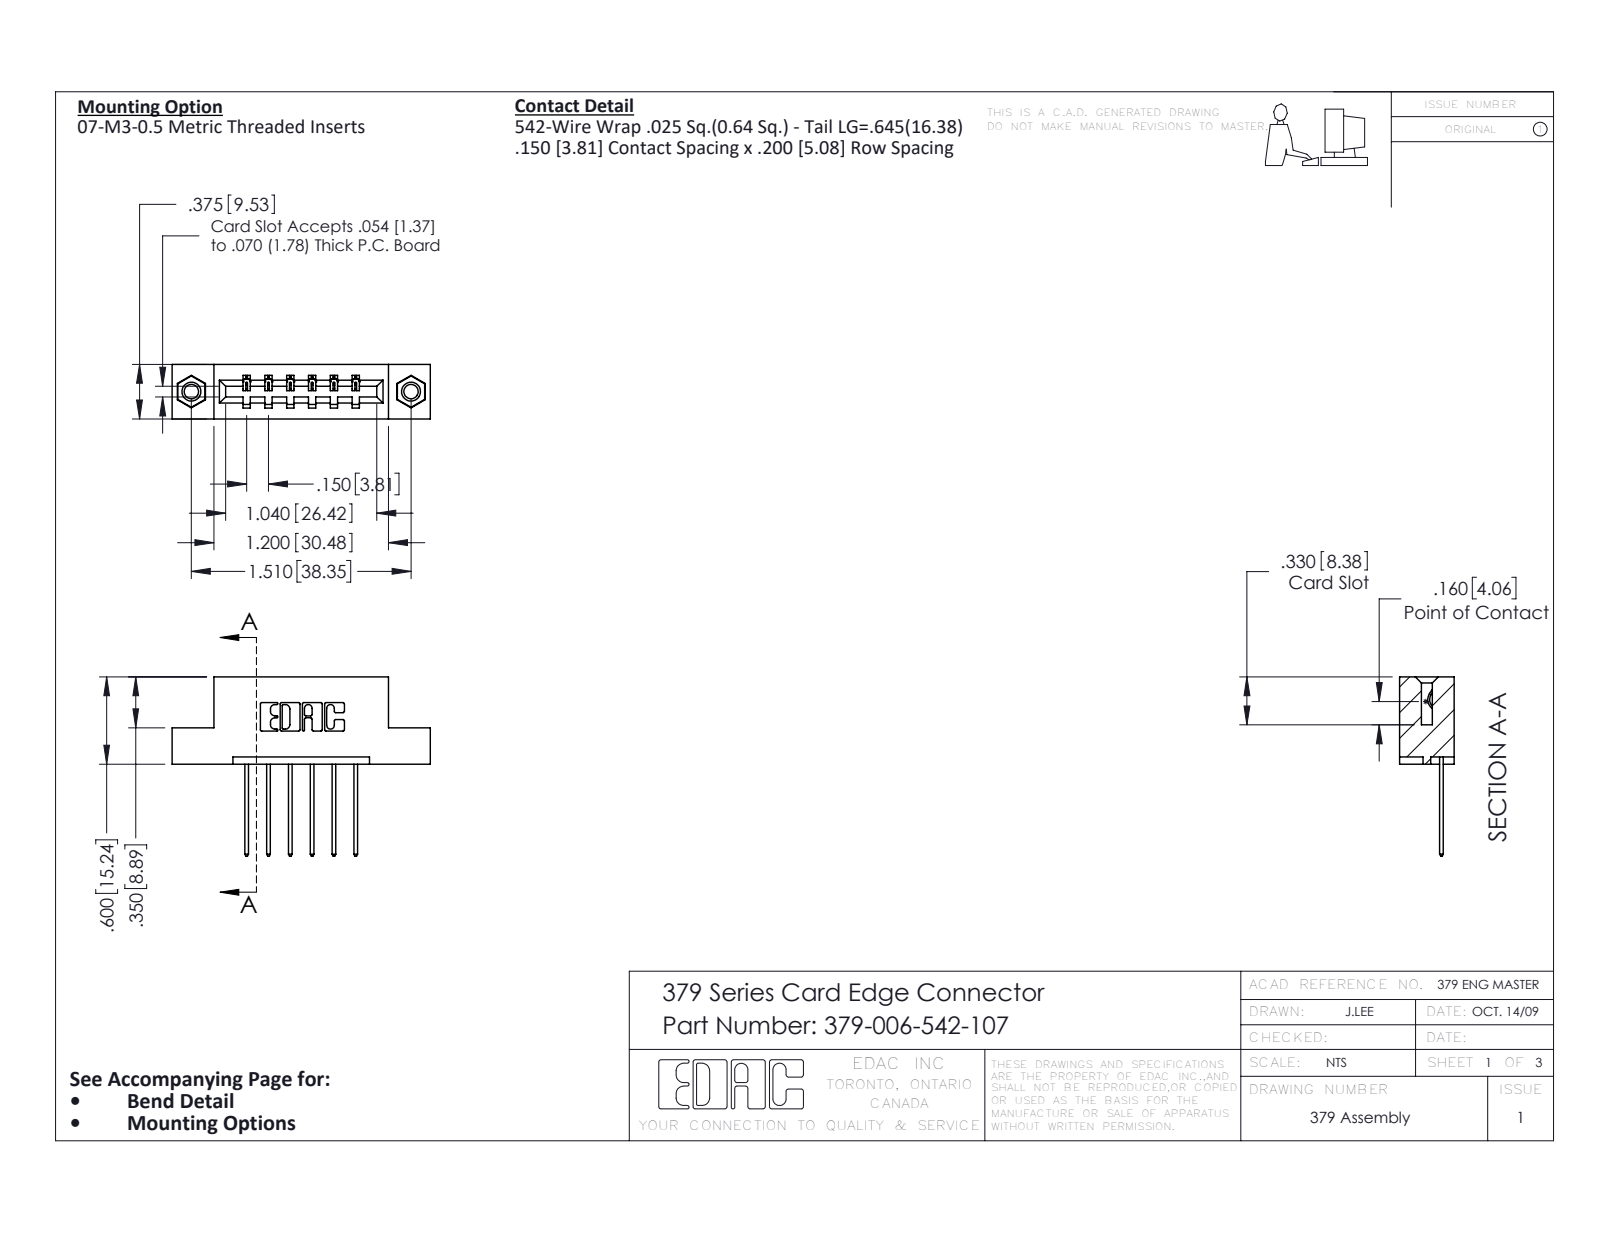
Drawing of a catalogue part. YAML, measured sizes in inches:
part_name: "345-250-001_345-250-005-103; 379 Part_Flush - .156 Dia - TI; 379-006-542-107; 345-292-001_345-293-142"
step_written_by: "SolidWorks 2016 (CONFIG_CONTROL_DESIGN)"
units: inches
bodies: {solids: 9, faces: 522, planar: 354, cylindrical: 152, other: 16}
overall_size: [1.775, 1.232, 0.375]
volume: 0.263
surface_area: 6.754
round_holes:
  - {diameter: 0.098, count: 2}
  - {diameter: 0.125, count: 2}
  - {diameter: 0.156, count: 2}
round_bosses_or_shafts:
  - {diameter: 0.155, count: 2}
partial_cylinders:
  - {radius: 0.01, count: 22}
  - {radius: 0.006, count: 12}
  - {radius: 0.01, count: 12}
  - {radius: 0.007, count: 6}
  - {radius: 0.031, count: 6}
  - {radius: 0.026, count: 3}
  - {radius: 0.014, count: 1}
  - {radius: 0.022, count: 1}
face_to_face_distances: [0.3, 0.2, 0.375, 0.05, 0.15, 0.075, 0.1, 0.25, 0.35, 0.6]
hole_center_spacings: [1.51]
